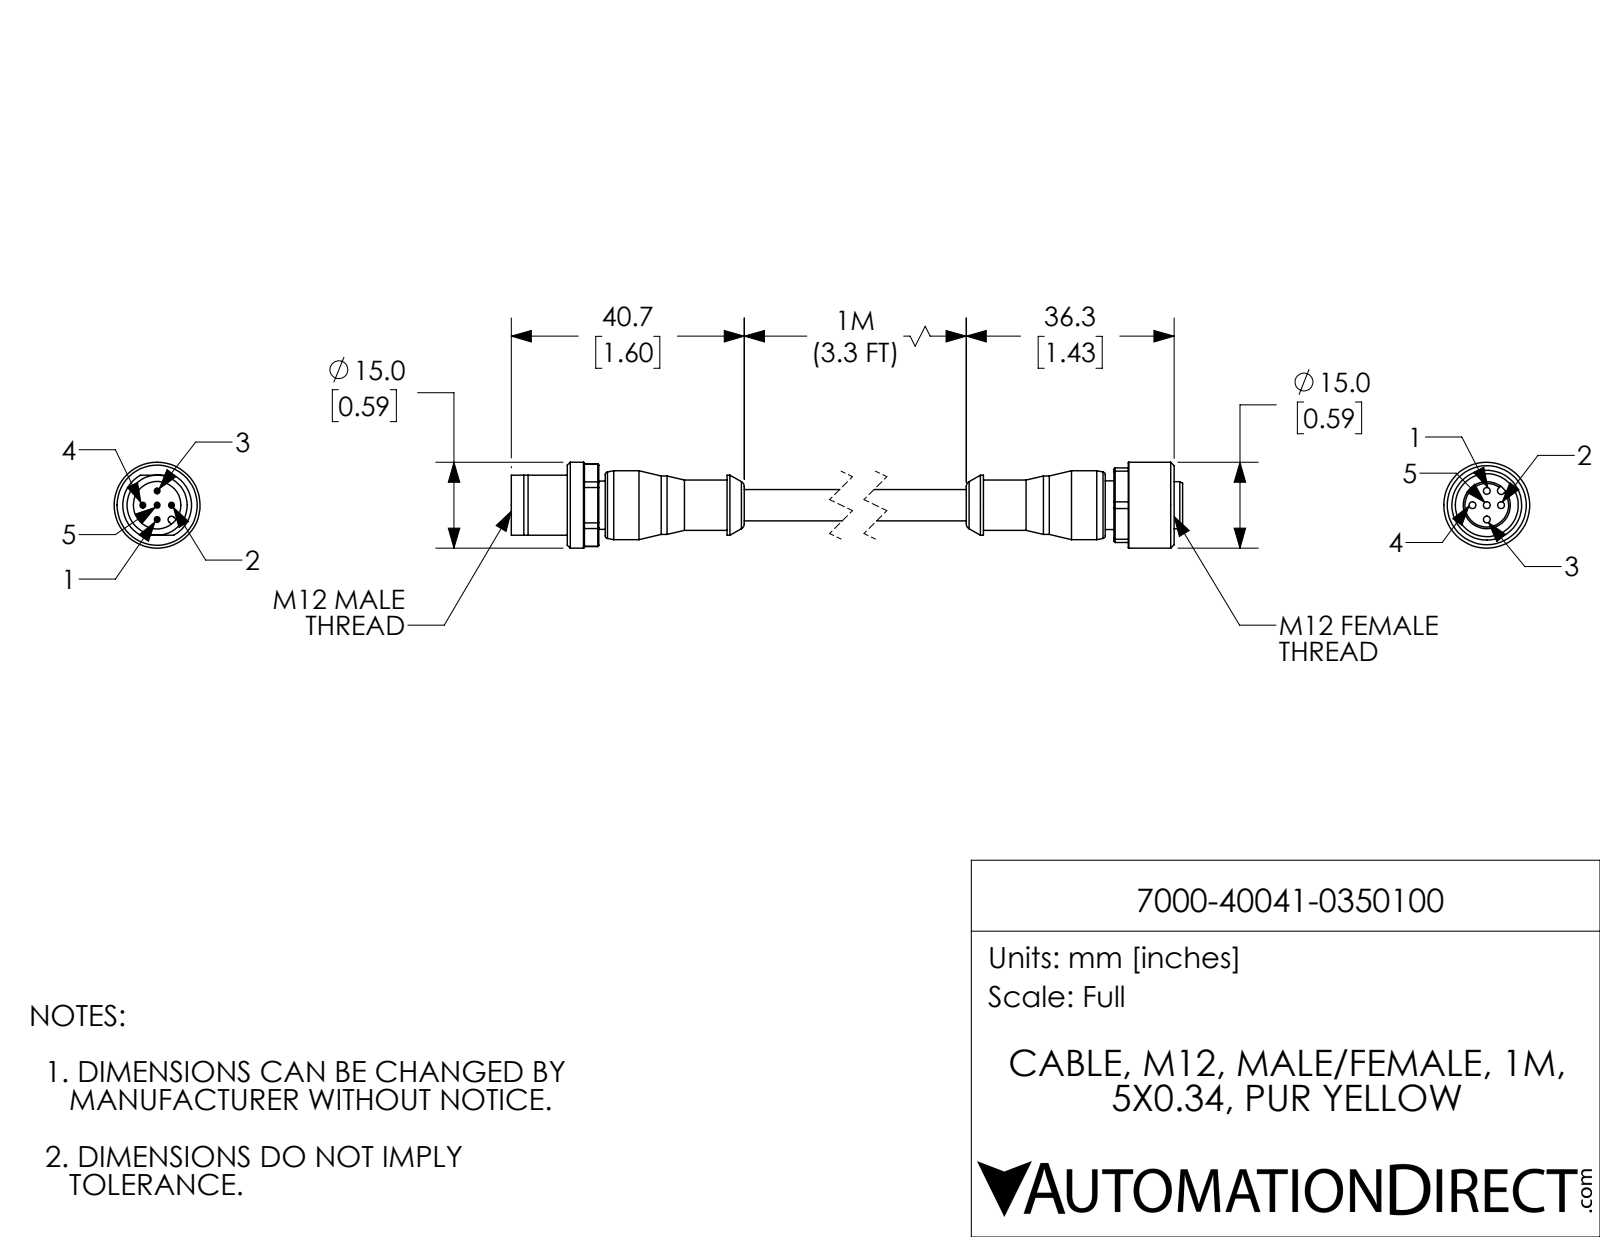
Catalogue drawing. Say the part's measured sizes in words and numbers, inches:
The part is named "7000-40041-0350100; 7000-40041-0350100_FEMALE; 7000-40041-0350100_MALE". Its 3-D file was written by "SolidWorks 2021 (CONFIG_CONTROL_DESIGN)". It is 2 solids with 196 faces: 60 planar, 73 cylindrical and 63 other. Overall it measures 5.138 by 0.591 by 0.591 inches. Its volume is 0.488 cubic inches and its surface area 8.004 square inches. Round holes: 5 of diameter 0.047, 1 of diameter 0.327, 1 of diameter 0.433. Round bosses or shafts: 5 of diameter 0.039, 1 of diameter 0.591, 1 of diameter 0.472, 1 of diameter 0.413, 1 of diameter 0.402, 1 of diameter 0.346, 1 of diameter 0.335, 1 of diameter 0.331. Partial cylindrical surfaces (rounded edges, fillets, slot ends): 1 of radius 0.024, 1 of radius 0.026, 1 of radius 0.283. The main face-to-face distances are 0.472, 0.512, 0.118, 4.063, 0.413, 4.433, 2.217, 4.28, 0.295, 0.059. The hole center spacings are 0.098, 0.139, 0.197.
